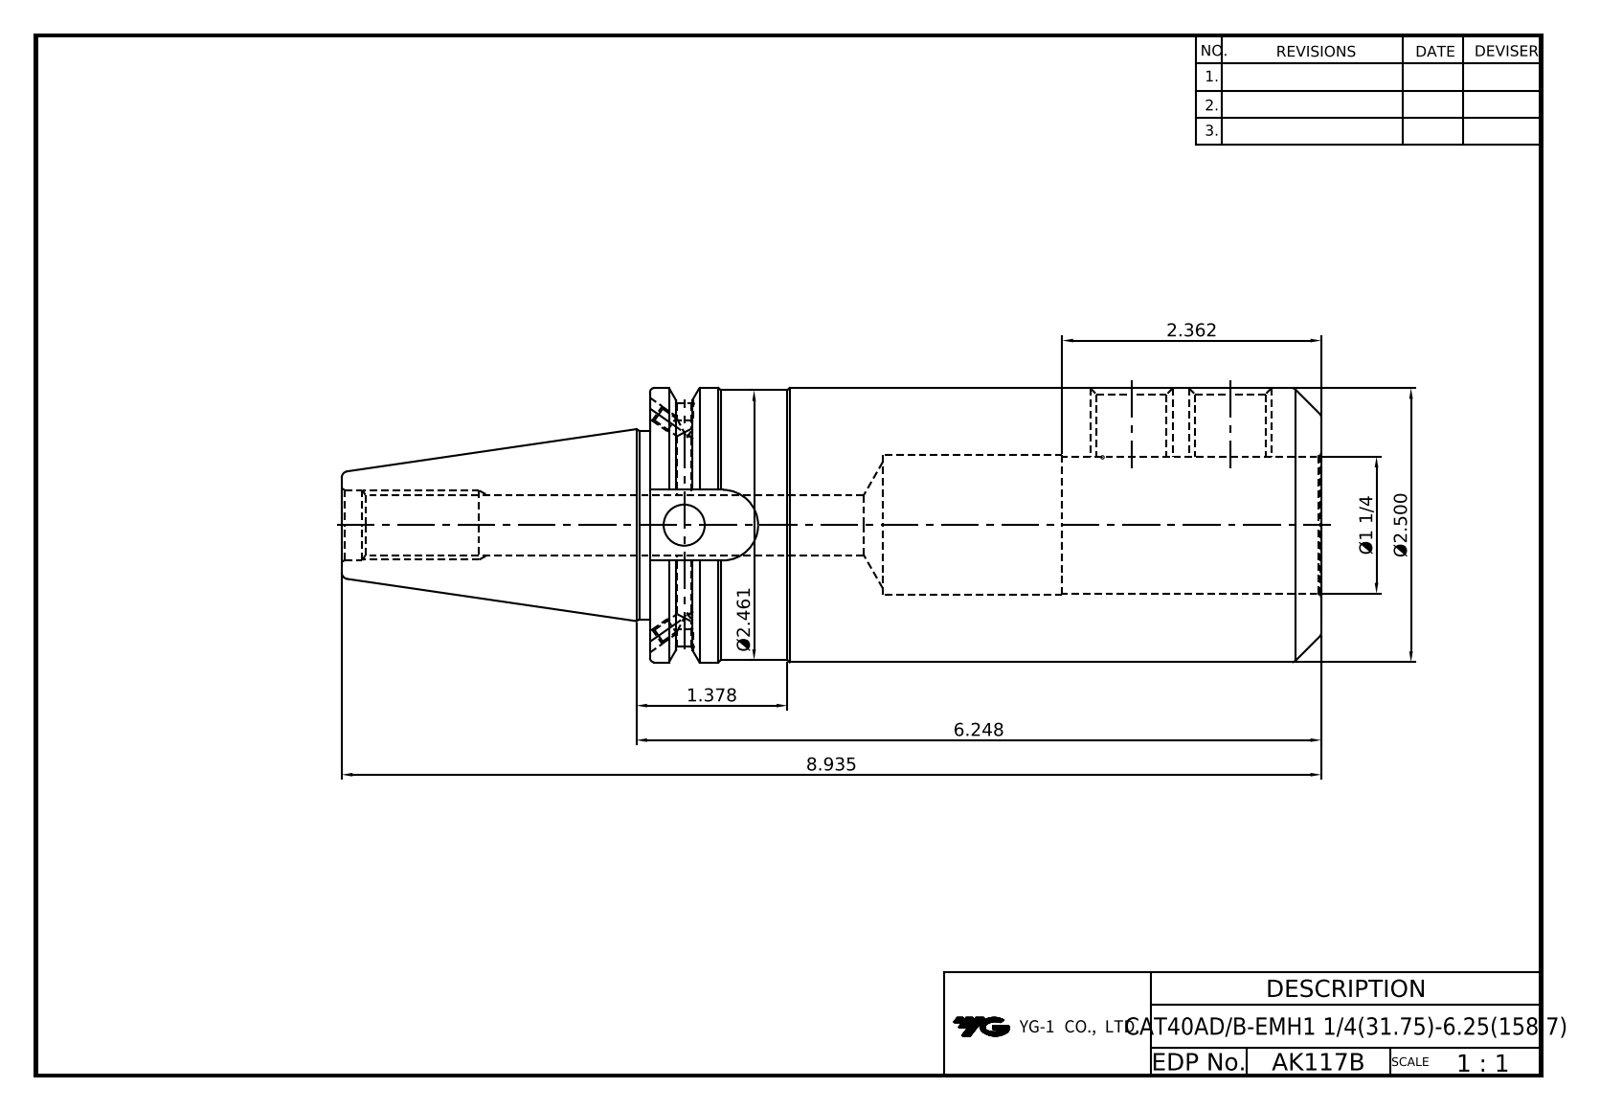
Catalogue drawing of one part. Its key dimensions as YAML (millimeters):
part_name: "LO-CAT40ADB-EMH31.75-158.7"
step_written_by: "Autodesk Inventor 2025 (AUTOMOTIVE_DESIGN)"
units: millimeters
bodies: {solids: 1, faces: 93, planar: 34, cylindrical: 32, other: 27}
overall_size: [226.95, 63.5, 63.5]
volume: 438840
surface_area: 61320
round_holes:
  - {diameter: 3.24, count: 4}
  - {diameter: 4, count: 2}
  - {diameter: 4.2, count: 2}
  - {diameter: 17.32, count: 2}
  - {diameter: 9.53, count: 1}
  - {diameter: 13.39, count: 1}
  - {diameter: 16.3, count: 1}
  - {diameter: 31.75, count: 1}
  - {diameter: 32.95, count: 1}
round_bosses_or_shafts:
  - {diameter: 63.5, count: 1}
  - {diameter: 62.5, count: 1}
  - {diameter: 43.6, count: 1}
partial_cylinders:
  - {radius: 8.19, count: 1}
  - {radius: 28.15, count: 1}
face_to_face_distances: [155.53, 53.93, 101.6, 47.6, 16.38, 71.42, 125.35, 226.95, 81.29, 9.87]
hole_center_spacings: [22.86]
